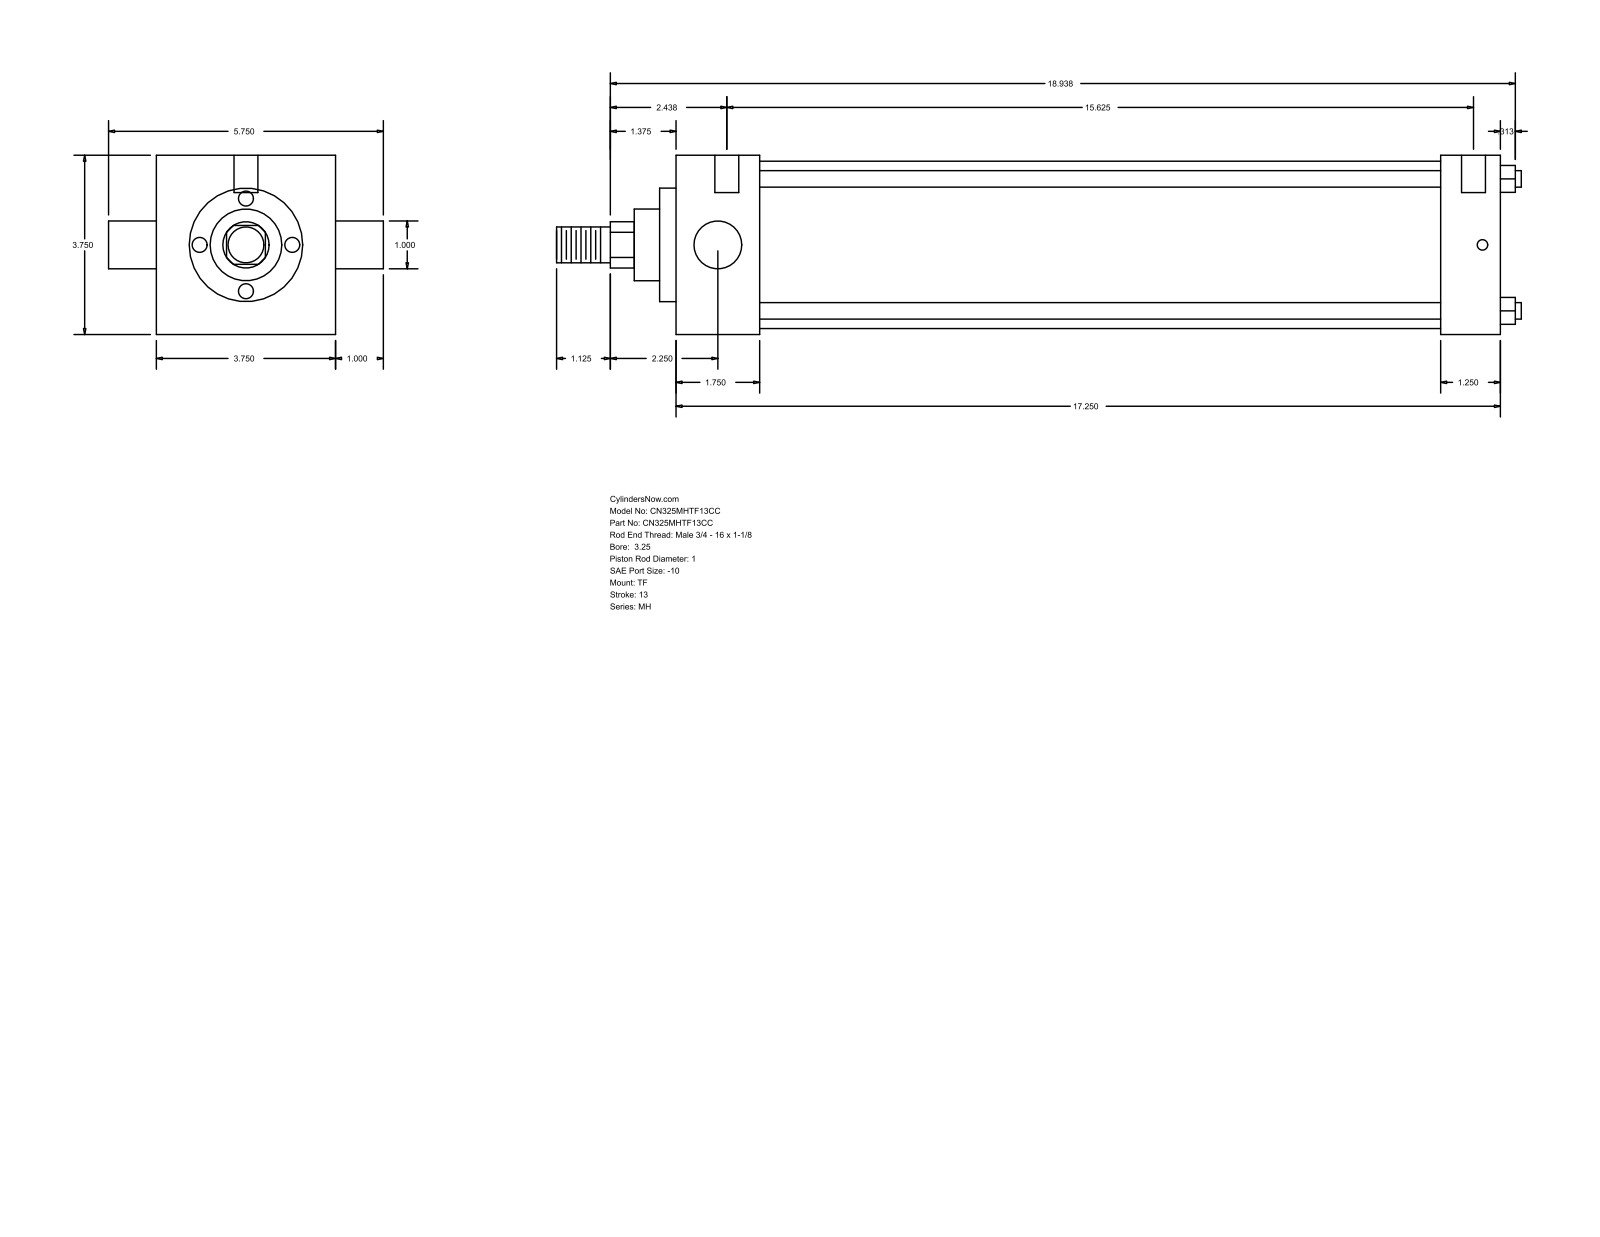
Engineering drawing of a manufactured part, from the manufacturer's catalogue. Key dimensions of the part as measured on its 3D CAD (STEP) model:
Part name (STEP PRODUCT): MH_TF__0325_1
STEP written by: GSSL Pune (CONFIG_CONTROL_DESIGN)
Units: millimetres
Bodies: 0 solids, 86 faces (61 planar, 25 cylindrical, 0 other)
Overall size (bounding box): 512.76 × 146.05 × 95.25
Round holes (diameter × count): ⌀5.56 ×3, ⌀12.7 ×2
Round bosses / shafts (diameter × count): ⌀8.76 ×4, ⌀25.4 ×2, ⌀88.9 ×1, ⌀60.33 ×1, ⌀38.1 ×1, ⌀19.05 ×1
Partial cylindrical surfaces — rounded edges, fillets, slot ends (radius × count): R12.29 ×1
Main face-to-face distances: 95.24, 438.15, 44.46, 406.4, 361.94, 393.69, 31.75, 8.73, 53.19, 415.13
Hole centre spacings: 1.58, 4.76, 396.88, 398.46, 401.64, 403.22
